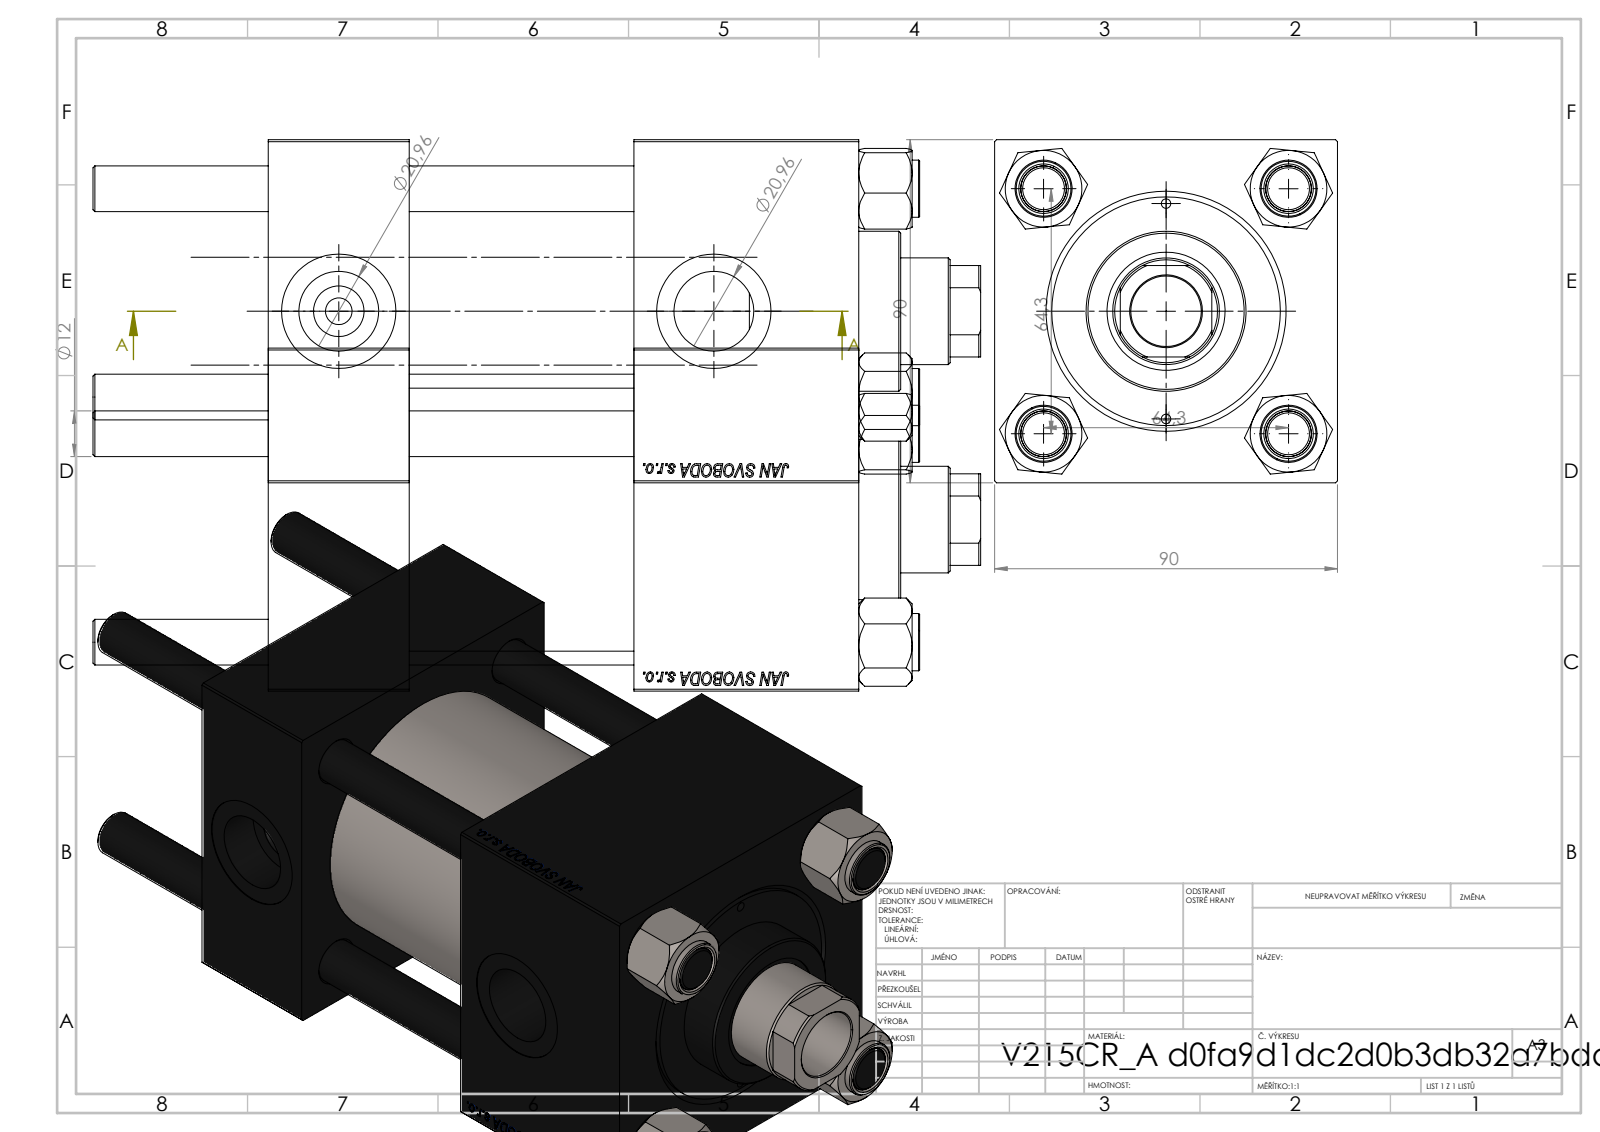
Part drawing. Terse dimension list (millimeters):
name: V215CR_BODY_A; V215CR_VCP; CR025_012_A_0_G_A_G_M_020_+#_##_TYCINKA; V215_VC_A (+1 more)
written by: SolidWorks 2019 (CONFIG_CONTROL_DESIGN)
unit: mm
bodies: 11 solids, 1140 faces (521 planar, 83 cylindrical, 536 other)
size: 233 × 90 × 90
volume: 979 804 mm³; area: 195 798 mm²
holes: 4× ⌀12, 2× ⌀2.5, 2× ⌀7, 2× ⌀20.96, 2× ⌀30, 1× ⌀18.5, 1× ⌀28, 1× ⌀31, 1× ⌀50, 1× ⌀60, 1× ⌀63
bosses: 4× ⌀15, 1× ⌀69, 1× ⌀42
rounds: 1× R13.5
face distances: 90, 59, 37, 155, 118, 96, 126.3, 89.3, 30.3, 28.7
hole spacings: 32.39, 45.47, 64.3, 68.42, 28.25, 90.93, 56.5, 98.46
